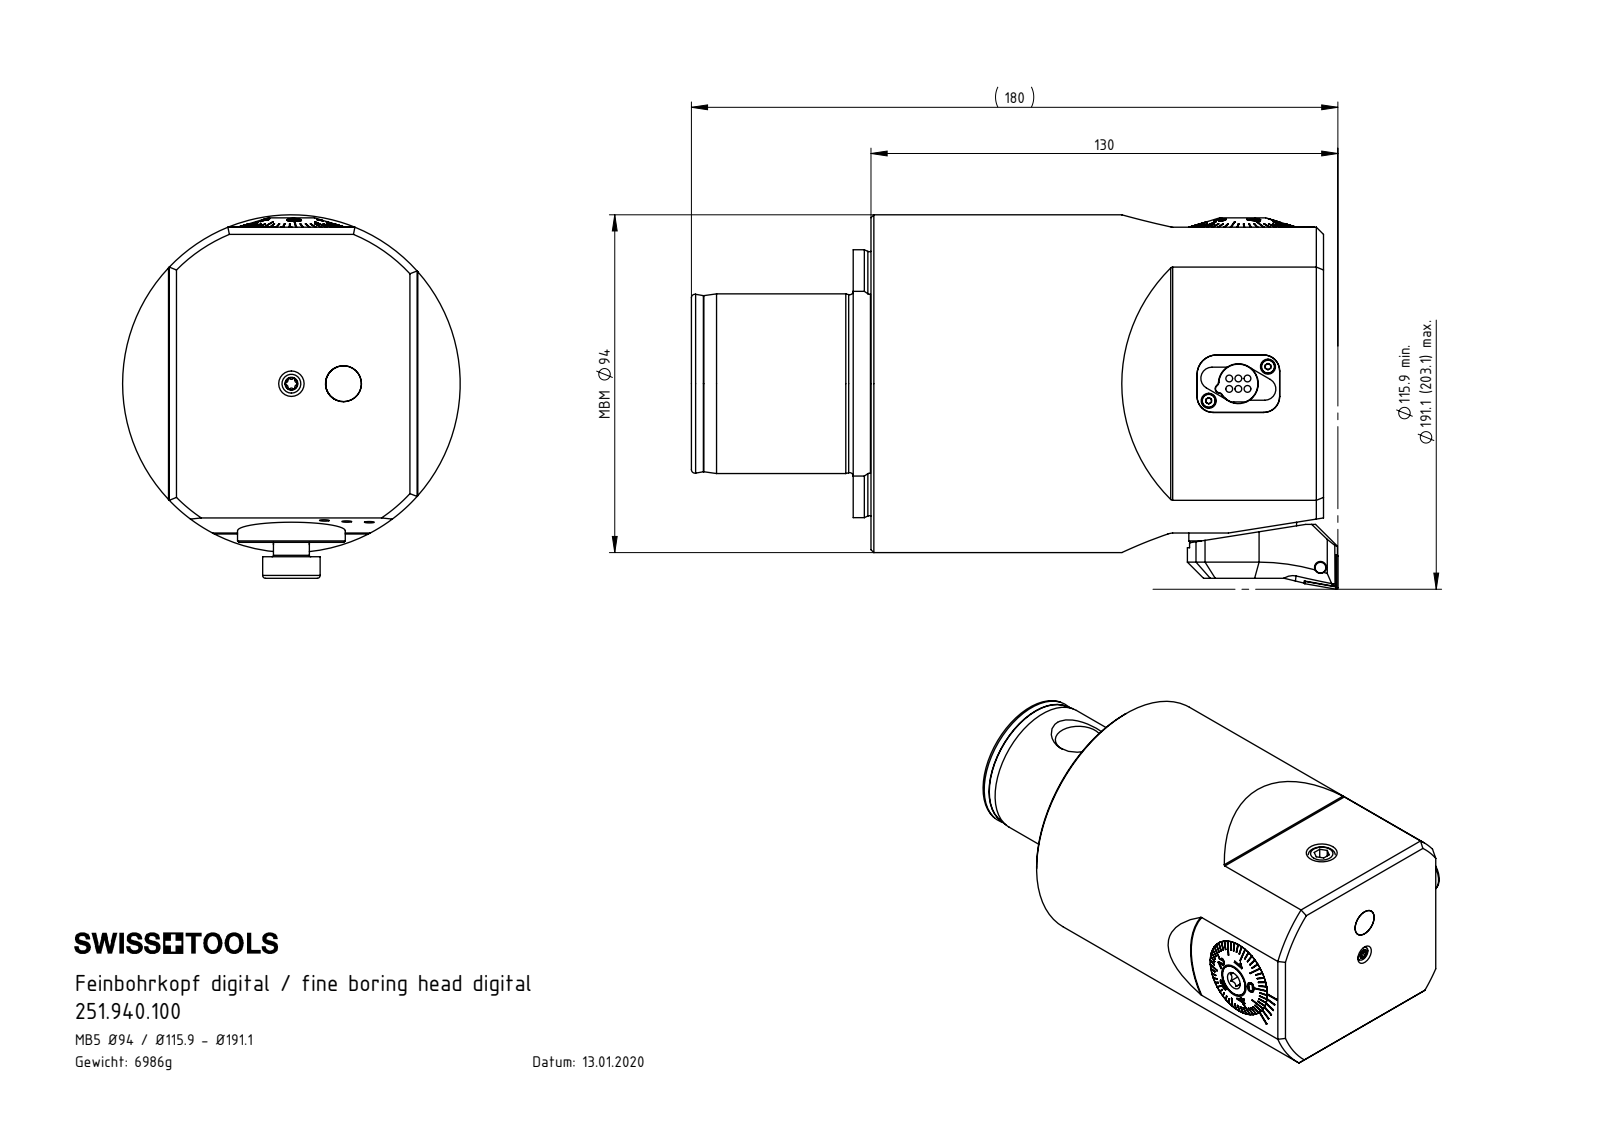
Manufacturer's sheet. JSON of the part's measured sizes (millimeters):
{"part_name": "MB9-F94.DA1.130_A; F55-WCB.001.013_D_fertigbearbeitet; CCMT09T304; WCB-ER2.001.009_A (+8 more)", "step_written_by": "SolidWorks 2017 (CONFIG_CONTROL_DESIGN)", "units": "millimeters", "bodies": {"solids": 28, "faces": 1178, "planar": 487, "cylindrical": 276, "other": 415}, "overall_size": [180, 104.6, 94], "volume_mm3": 828953, "surface_area_mm2": 111713, "round_holes": [[3.3, 9], [13.5, 4], [4.2, 3], [1.6, 2], [2.2, 2], [8.5, 2], [13, 2], [4.4, 1], [5, 1], [6.1, 1], [8, 1], [9.5, 1]], "round_bosses_or_shafts": [[1.9, 6], [10, 2], [5.25, 2], [4, 2], [3.8, 2], [2, 2], [94, 1], [50, 1]], "partial_cylinders_radius": [[0.34, 12], [0.59, 12], [1.2, 8], [1.1, 6], [0.5, 4], [4.5, 4], [3.2, 3], [4.4, 3]], "face_to_face_distances": [69, 126, 50, 176, 45.05, 4.95, 130.95, 81.6, 49.85, 4.8], "hole_center_spacings": [38, 9.52, 16.45, 5.72, 5.86, 9.98, 14.5, 19.04]}
